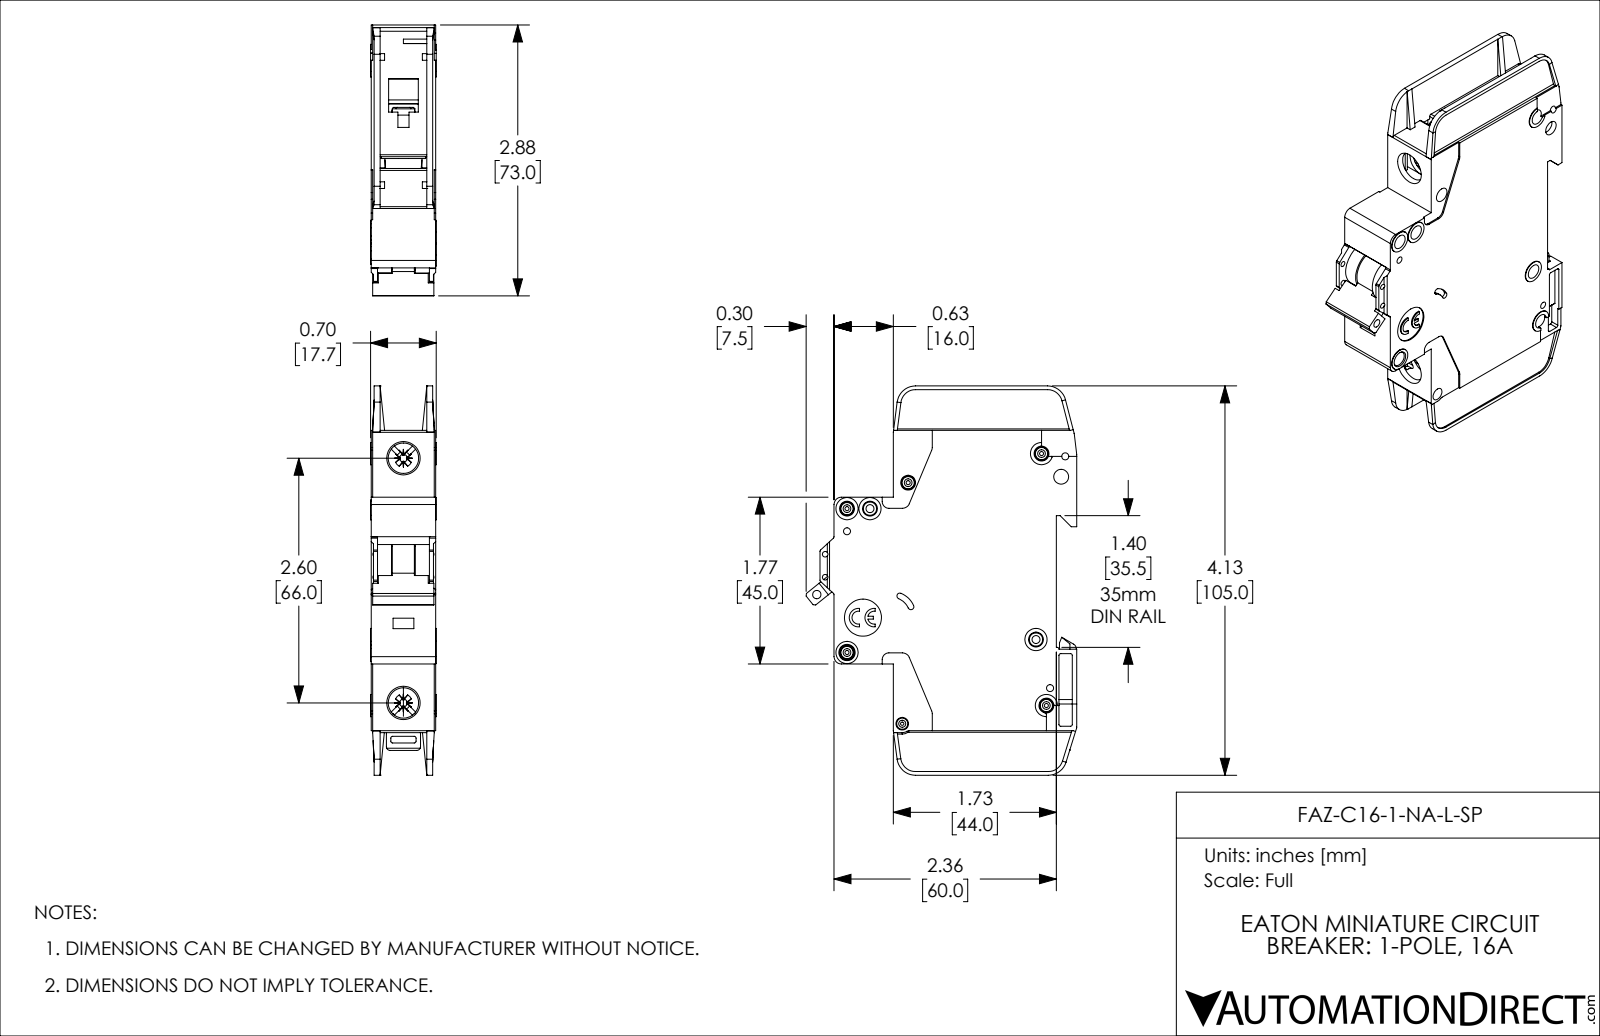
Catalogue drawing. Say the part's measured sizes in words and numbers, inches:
The part is named "FAZ-C16-1-NA-L-SP". Its 3-D file was written by "SolidWorks 2019 (AUTOMOTIVE_DESIGN)". It is 1 solid with 1127 faces: 671 planar, 357 cylindrical and 99 other. Overall it measures 4.134 by 2.876 by 0.697 inches. Its volume is 4.682 cubic inches and its surface area 41.01 square inches. Round holes: 8 of diameter 0.157, 5 of diameter 0.043, 4 of diameter 0.075, 2 of diameter 0.059, 2 of diameter 0.085, 2 of diameter 0.323, 1 of diameter 0.035, 1 of diameter 0.089, 1 of diameter 0.098, 1 of diameter 0.134, 1 of diameter 0.394. Round bosses or shafts: 5 of diameter 0.13, 4 of diameter 0.236, 2 of diameter 0.118, 1 of diameter 0.098. Partial cylindrical surfaces (rounded edges, fillets, slot ends): 42 of radius 0.02, 10 of radius 0.016, 10 of radius 0.039, 8 of radius 0.079, 5 of radius 0.197, 4 of radius 0.008, 4 of radius 0.026, 4 of radius 0.043. The main face-to-face distances are 0.047, 0.685, 0.591, 0.638, 0.094, 0.543, 0.016, 0.031, 0.496, 0.575. The hole center spacings are 0.244, 0.537, 0.87, 0.189, 0.199, 0.204, 0.221, 0.24.
